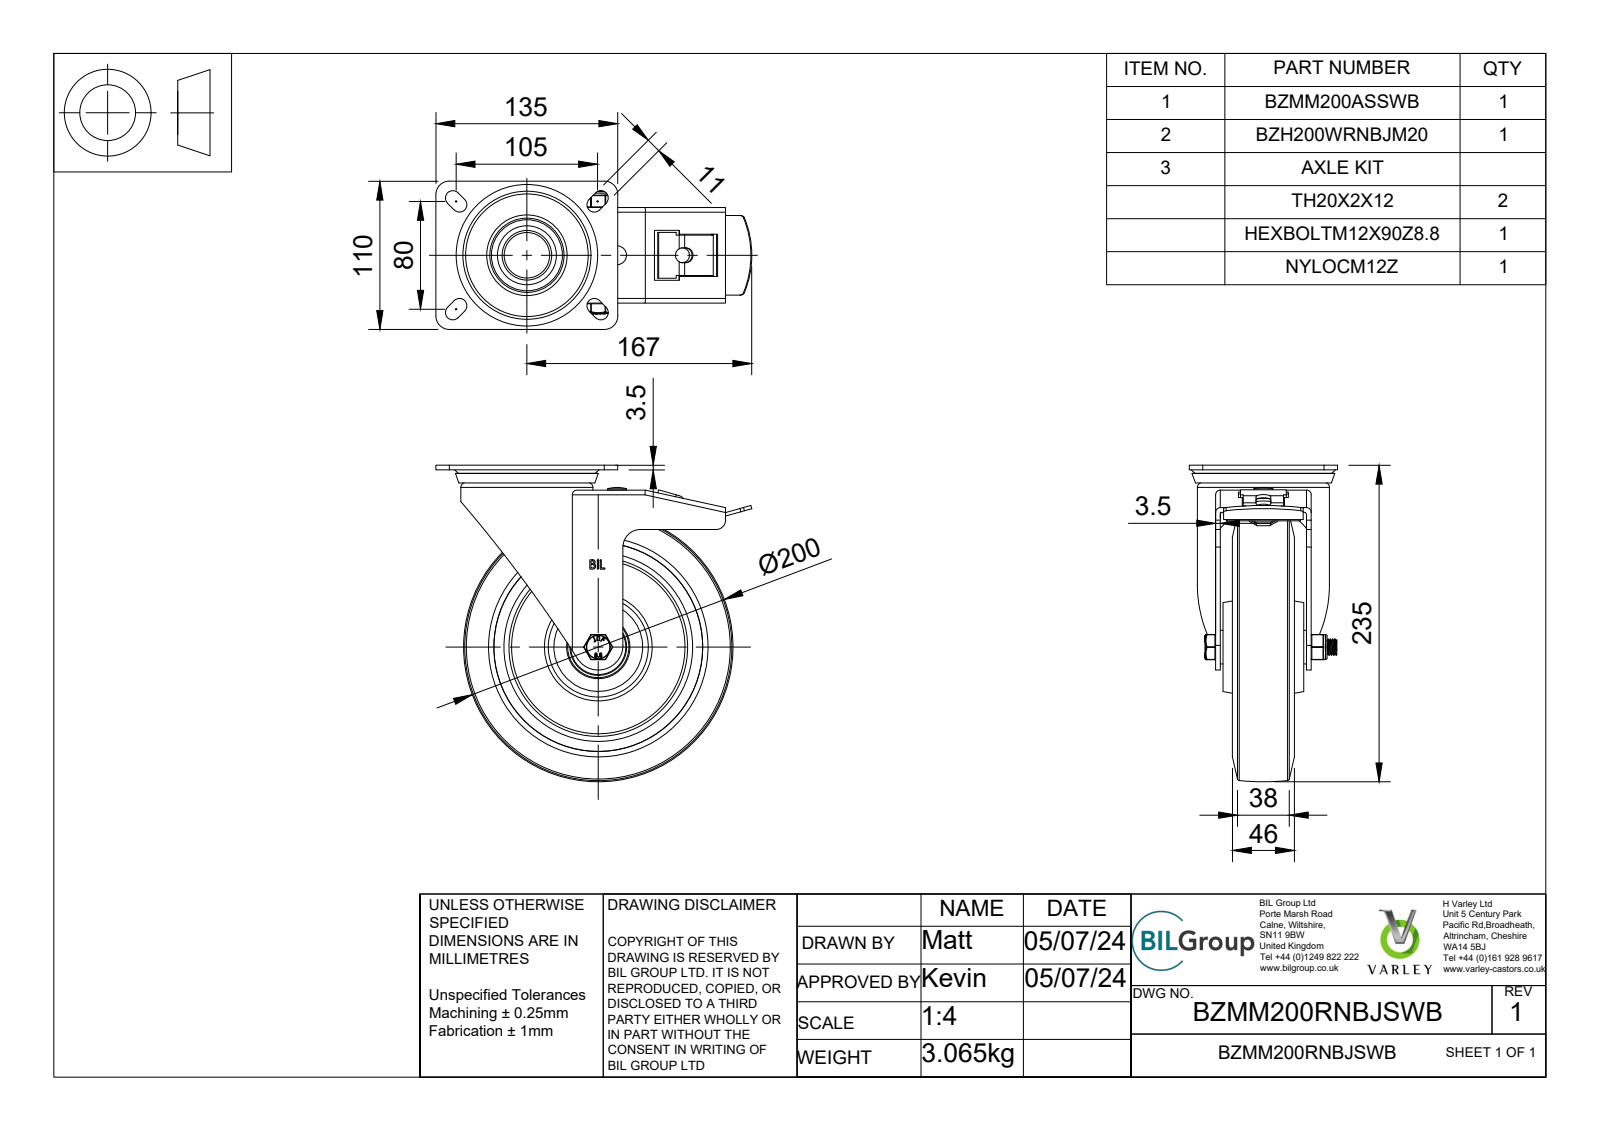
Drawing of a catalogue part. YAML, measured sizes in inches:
part_name: "BZMM200RNBJSWB v4; BZMM200ASSWB - 64 v1; ZINC PLATED, PRESSED STEEL TOP PLATE; ZINC PLATED, PRESSED STEEL TOP PLATE Geometry (+7 more)"
step_written_by: "Autodesk Translation Framework v13.14.0.145 (AUTOMOTIVE_DESIGN)"
units: inches
bodies: {solids: 82, faces: 1279, planar: 549, cylindrical: 244, other: 486}
overall_size: [9.252, 9.232, 4.331]
volume: 74.39
surface_area: 550
round_holes:
  - {diameter: 0.315, count: 1}
  - {diameter: 0.433, count: 1}
  - {diameter: 0.472, count: 1}
  - {diameter: 0.48, count: 1}
  - {diameter: 0.551, count: 1}
  - {diameter: 0.787, count: 1}
  - {diameter: 1.122, count: 1}
  - {diameter: 1.213, count: 1}
  - {diameter: 1.329, count: 1}
  - {diameter: 1.587, count: 1}
  - {diameter: 1.594, count: 1}
  - {diameter: 1.654, count: 1}
round_bosses_or_shafts:
  - {diameter: 3.858, count: 1}
  - {diameter: 3.071, count: 1}
  - {diameter: 1.969, count: 1}
  - {diameter: 1.606, count: 1}
  - {diameter: 1.565, count: 1}
  - {diameter: 1.232, count: 1}
  - {diameter: 1.063, count: 1}
  - {diameter: 0.984, count: 1}
partial_cylinders:
  - {radius: 0.02, count: 19}
  - {radius: 0.217, count: 10}
  - {radius: 0.069, count: 7}
  - {radius: 0.01, count: 6}
  - {radius: 0.098, count: 6}
  - {radius: 0.019, count: 4}
  - {radius: 0.035, count: 4}
  - {radius: 0.138, count: 4}
face_to_face_distances: [0.138, 0.354, 0.217, 0.492, 1.555, 0.512, 1.102, 1.417, 0.748, 1.24]
hole_center_spacings: [2.638]
